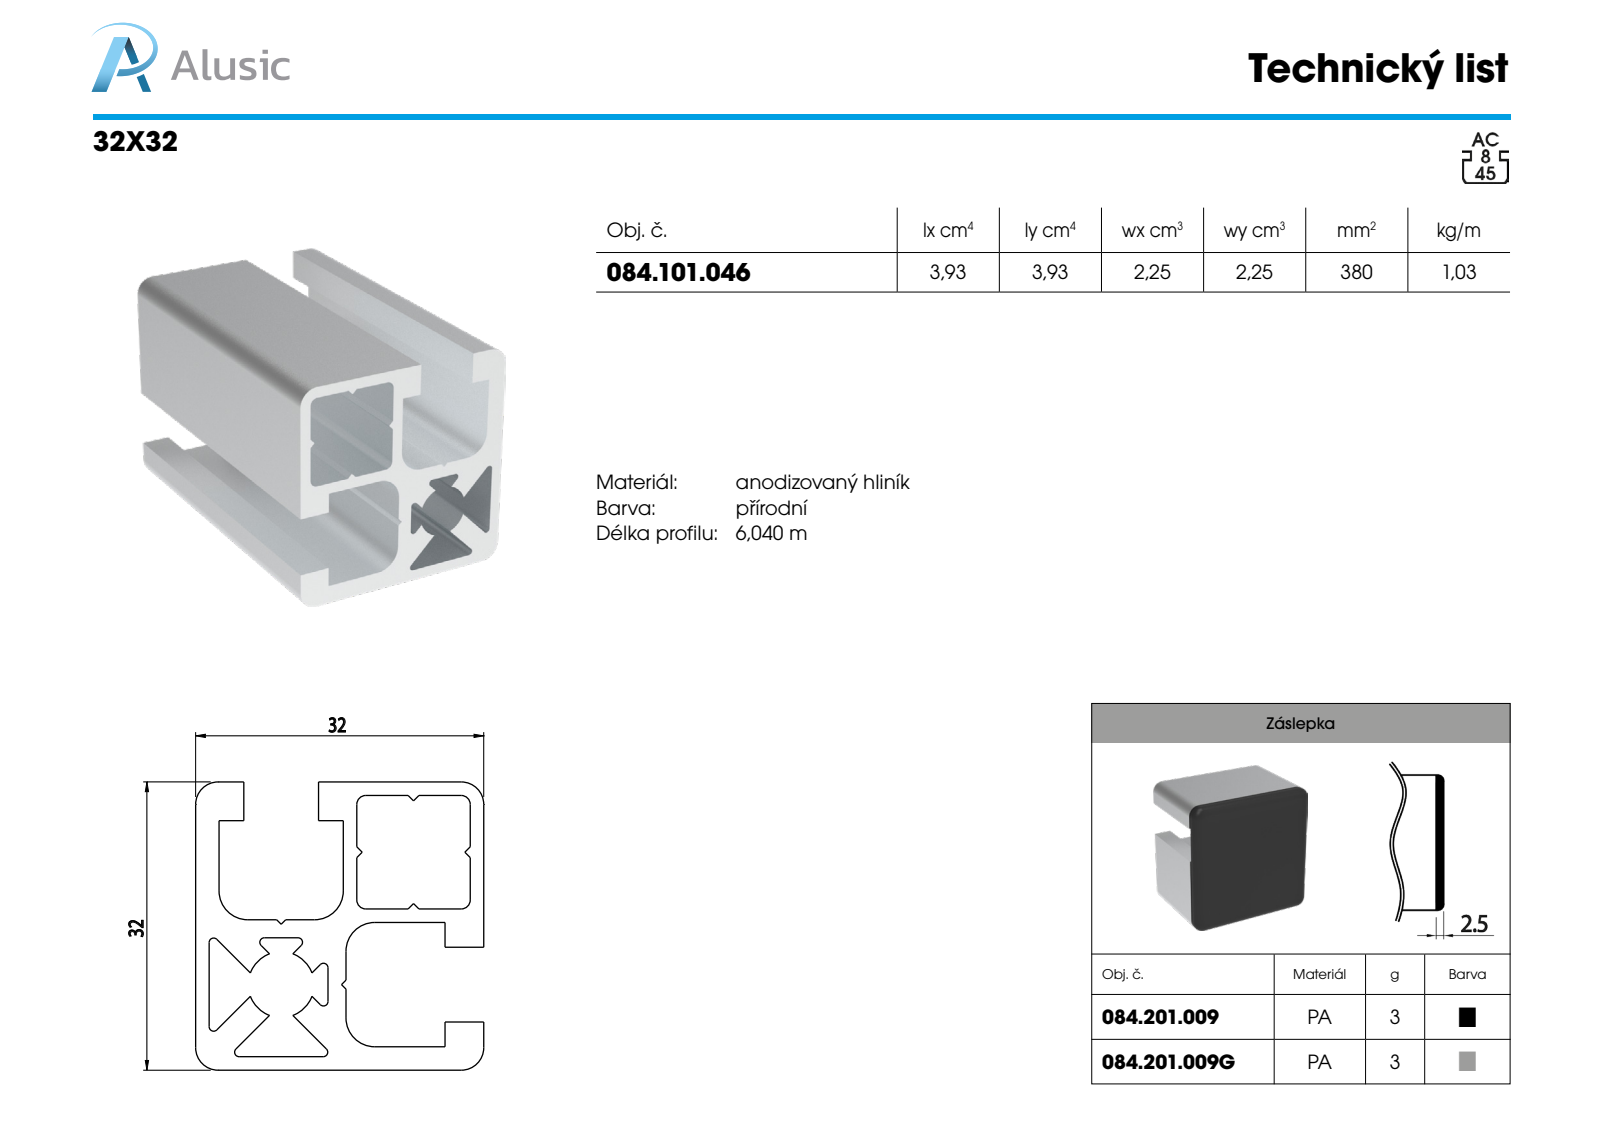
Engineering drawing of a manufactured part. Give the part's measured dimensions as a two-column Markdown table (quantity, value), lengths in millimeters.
| quantity | value |
| --- | --- |
| part name | 084.101.046 |
| STEP written by | SolidWorks 2018 (AUTOMOTIVE_DESIGN) |
| units | millimeters |
| bodies | 1 solid, 82 faces (56 planar, 26 cylindrical, 0 other) |
| overall size | 100 × 32 × 32 |
| volume | 37 635 mm³ |
| surface area | 33 480 mm² |
| partial cylindrical surfaces (radius × count) | 0.5 × 8, 1 × 4, 2.5 × 4, 3.2 × 4, 3.65 × 1 |
| main face-to-face distances | 1.5, 14.1, 30.5, 32, 16.4, 15.3, 13.8, 17.9, 12.6, 29 |
